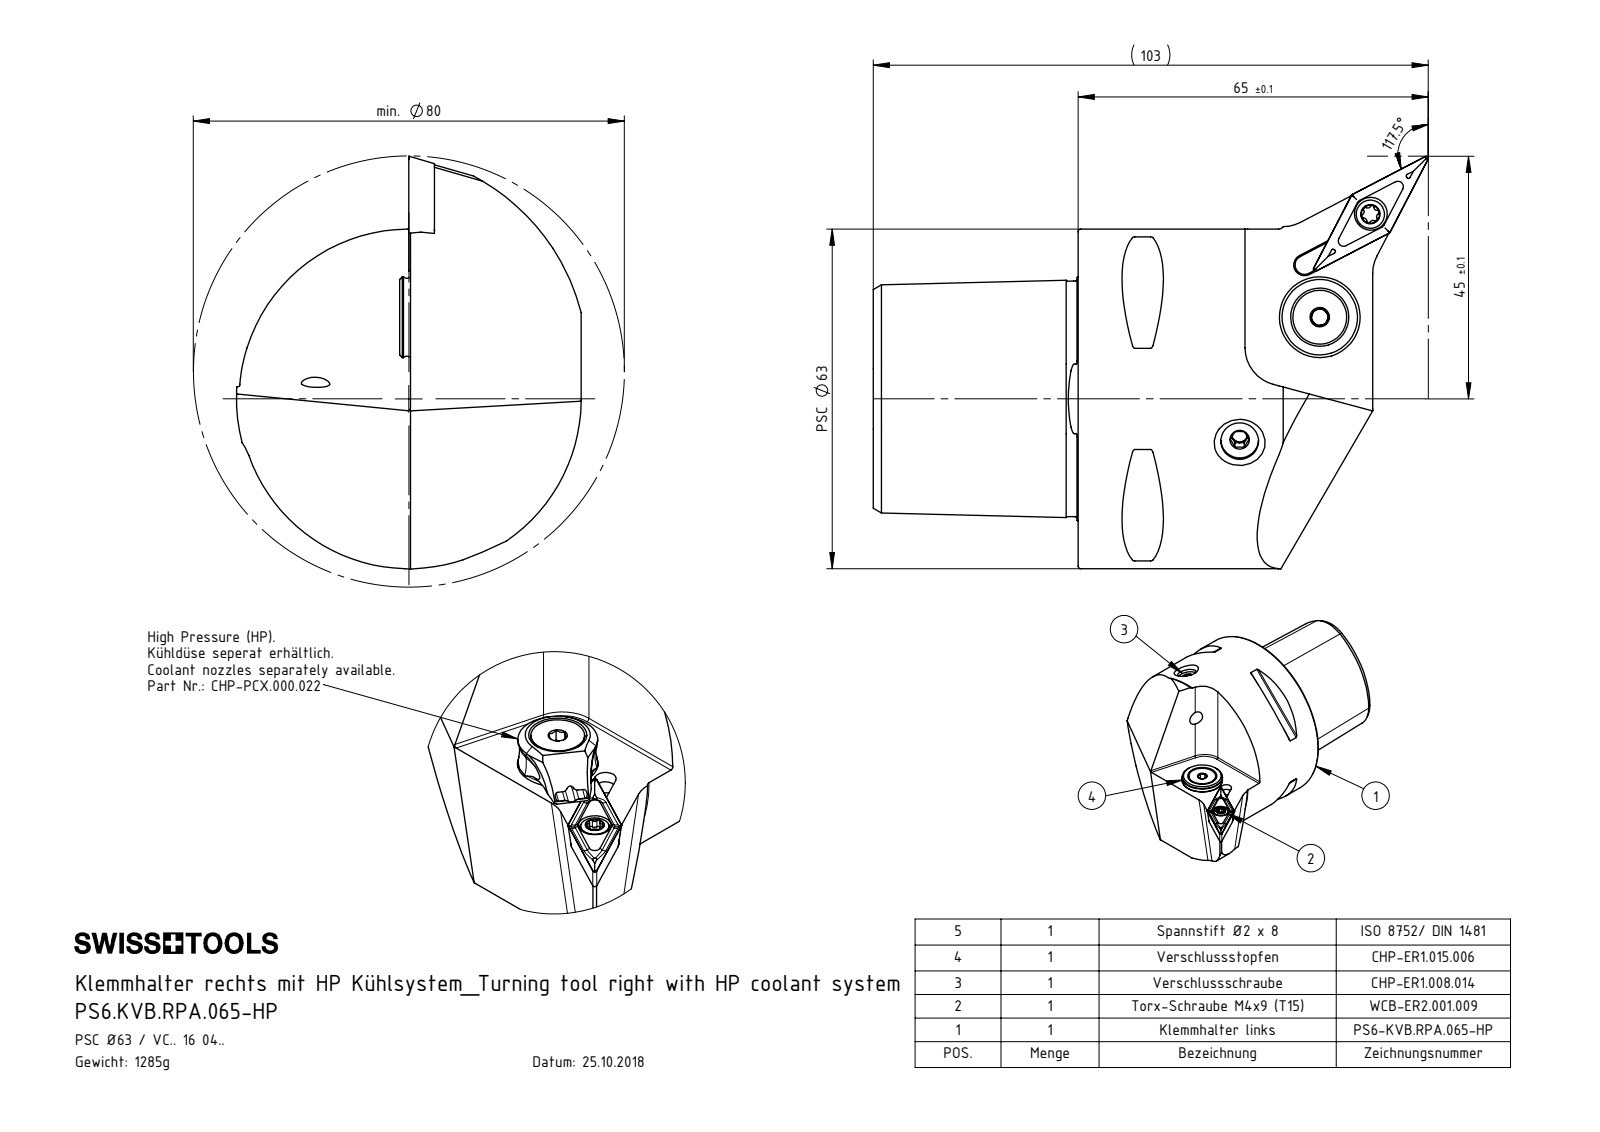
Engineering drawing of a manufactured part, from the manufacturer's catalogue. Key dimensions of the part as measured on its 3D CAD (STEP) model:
Part name (STEP PRODUCT): PS6.KVB.RPA.065-HP; ISO 8752 2x8; PS6-KVB.RPA.065-HP_A; CHP-ER1.008.014_A (+7 more)
STEP written by: SolidWorks 2017 (AUTOMOTIVE_DESIGN)
Units: millimetres
Bodies: 9 solids, 376 faces (105 planar, 93 cylindrical, 178 other)
Overall size (bounding box): 103 × 76.57 × 64
Volume: 163 655 mm³ · Surface area: 31 793 mm²
Round holes (diameter × count): ⌀4.2 ×2, ⌀5 ×2, ⌀1.2 ×1, ⌀2 ×1, ⌀3 ×1, ⌀3.3 ×1, ⌀4 ×1, ⌀4.4 ×1, ⌀5.3 ×1, ⌀6.1 ×1, ⌀7 ×1, ⌀8.1 ×1
Round bosses / shafts (diameter × count): ⌀63 ×1, ⌀14.85 ×1, ⌀13.4 ×1, ⌀10 ×1, ⌀8 ×1, ⌀5.5 ×1, ⌀5.25 ×1, ⌀5 ×1
Partial cylindrical surfaces — rounded edges, fillets, slot ends (radius × count): R0.5 ×12, R1 ×7, R0.34 ×6, R0.59 ×6, R6 ×3, R7 ×3, R1.1 ×2, R1.2 ×2
Main face-to-face distances: 31, 38, 69, 24.88, 11, 27, 42, 4.46, 27.24, 31.7
Hole centre spacings: 4.5, 18.5, 18.6, 21.29, 21.4, 27.5, 36.19, 40.66
